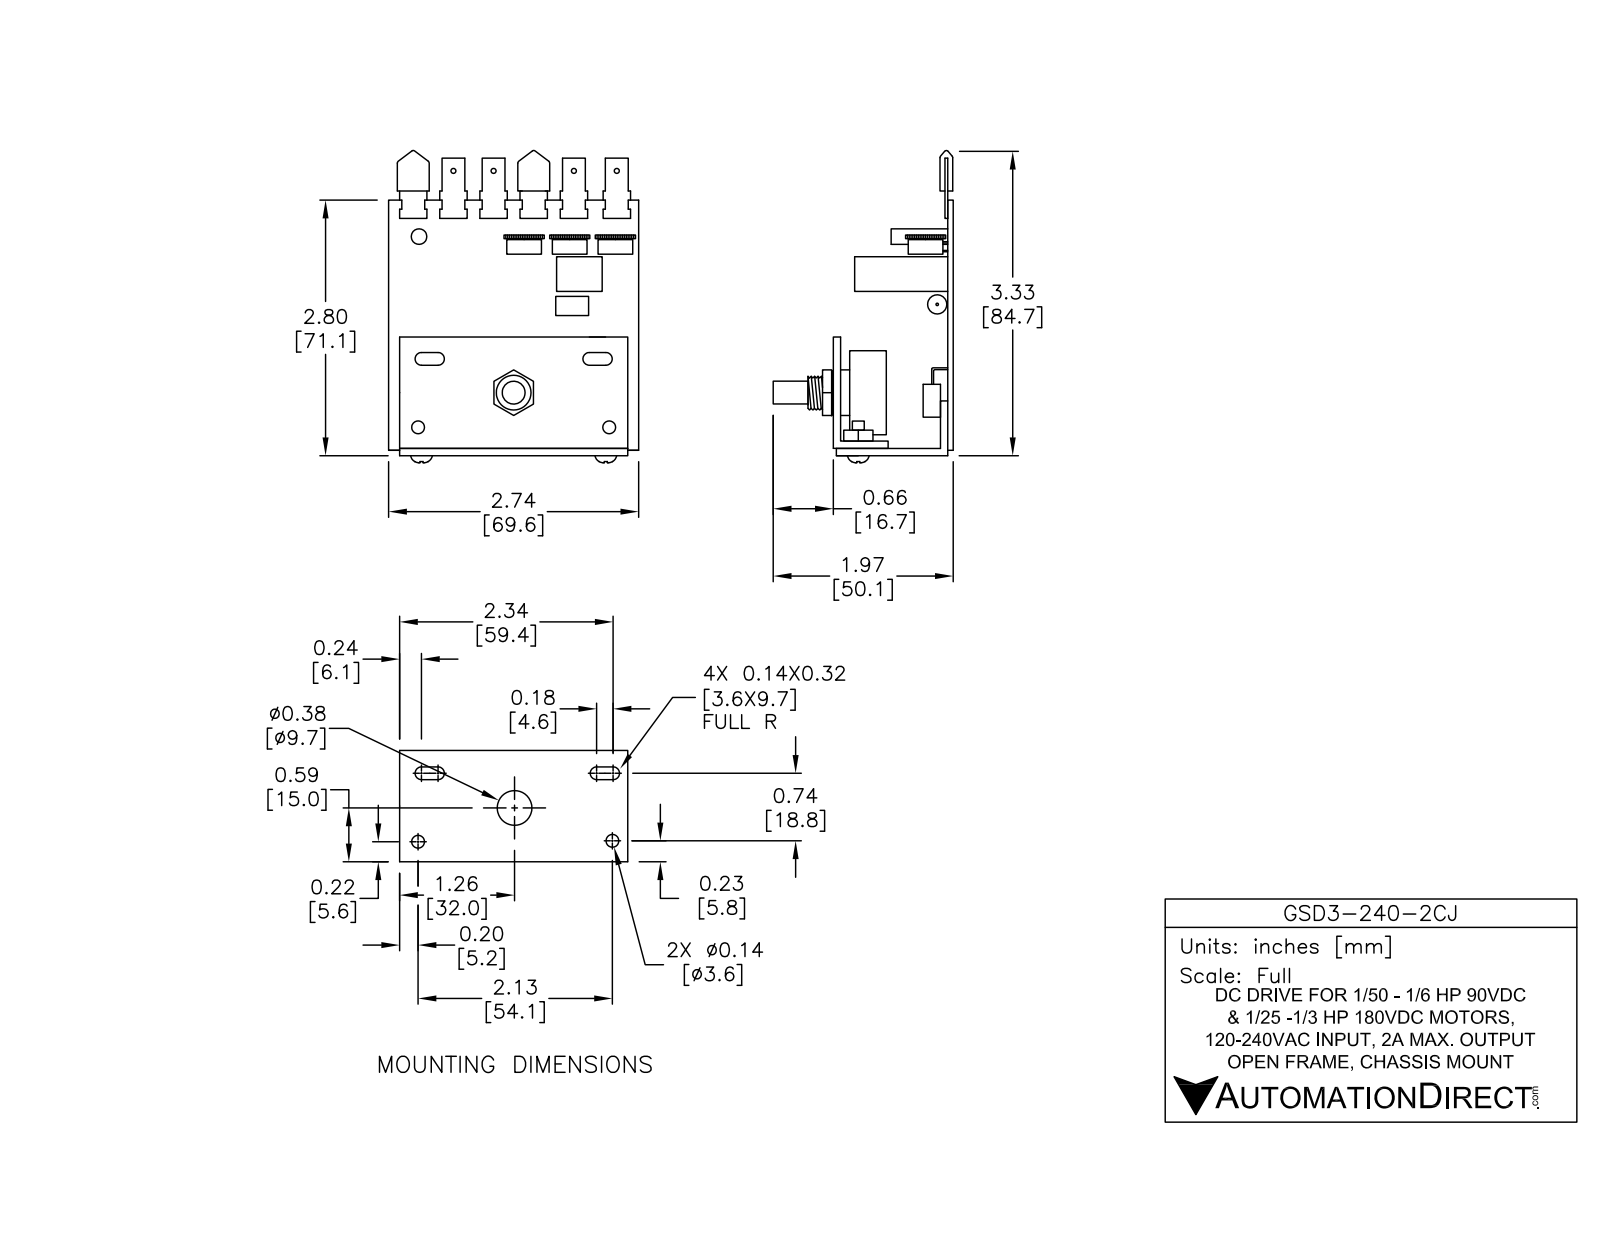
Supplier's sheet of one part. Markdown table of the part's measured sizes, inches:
| quantity | value |
| --- | --- |
| part name | Q4; SMT_DI_SOD-123_IPC; GSD3-240-2CJ; A-4-2705 (+7 more) |
| STEP written by | SolidWorks 2014 (AUTOMOTIVE_DESIGN) |
| units | inches |
| bodies | 112 solids, 3389 faces (2133 planar, 1060 cylindrical, 196 other) |
| overall size | 3.303 × 2.734 × 2.016 |
| volume | 2.16 in³ |
| surface area | 59.35 in² |
| round holes (diameter × count) | 0.026 × 22, 0.052 × 18, 0.033 × 15, 0.043 × 14, 0.046 × 14, 0.14 × 14, 0.067 × 11, 0.04 × 6, 0.08 × 4, 0.11 × 4, 0.144 × 4, 0.048 × 3 |
| round bosses / shafts (diameter × count) | 0.022 × 8, 0.026 × 6, 0.025 × 6, 0.25 × 5, 0.156 × 4, 0.354 × 3, 0.106 × 3, 0.051 × 3 |
| partial cylindrical surfaces (radius × count) | 0.004 × 48, 0.025 × 23, 0.05 × 12, 0.02 × 8, 0.07 × 8, 0.039 × 4, 0.091 × 4, 0.225 × 3 |
| main face-to-face distances | 0.08, 0.063, 1.15, 1.23, 1.293, 1.213, 1.07, 0.143, 0.16, 1.195 |
| hole center spacings | 0.15, 0.3, 0.451, 0.58, 0.801, 0.151, 0.225, 0.233 |
